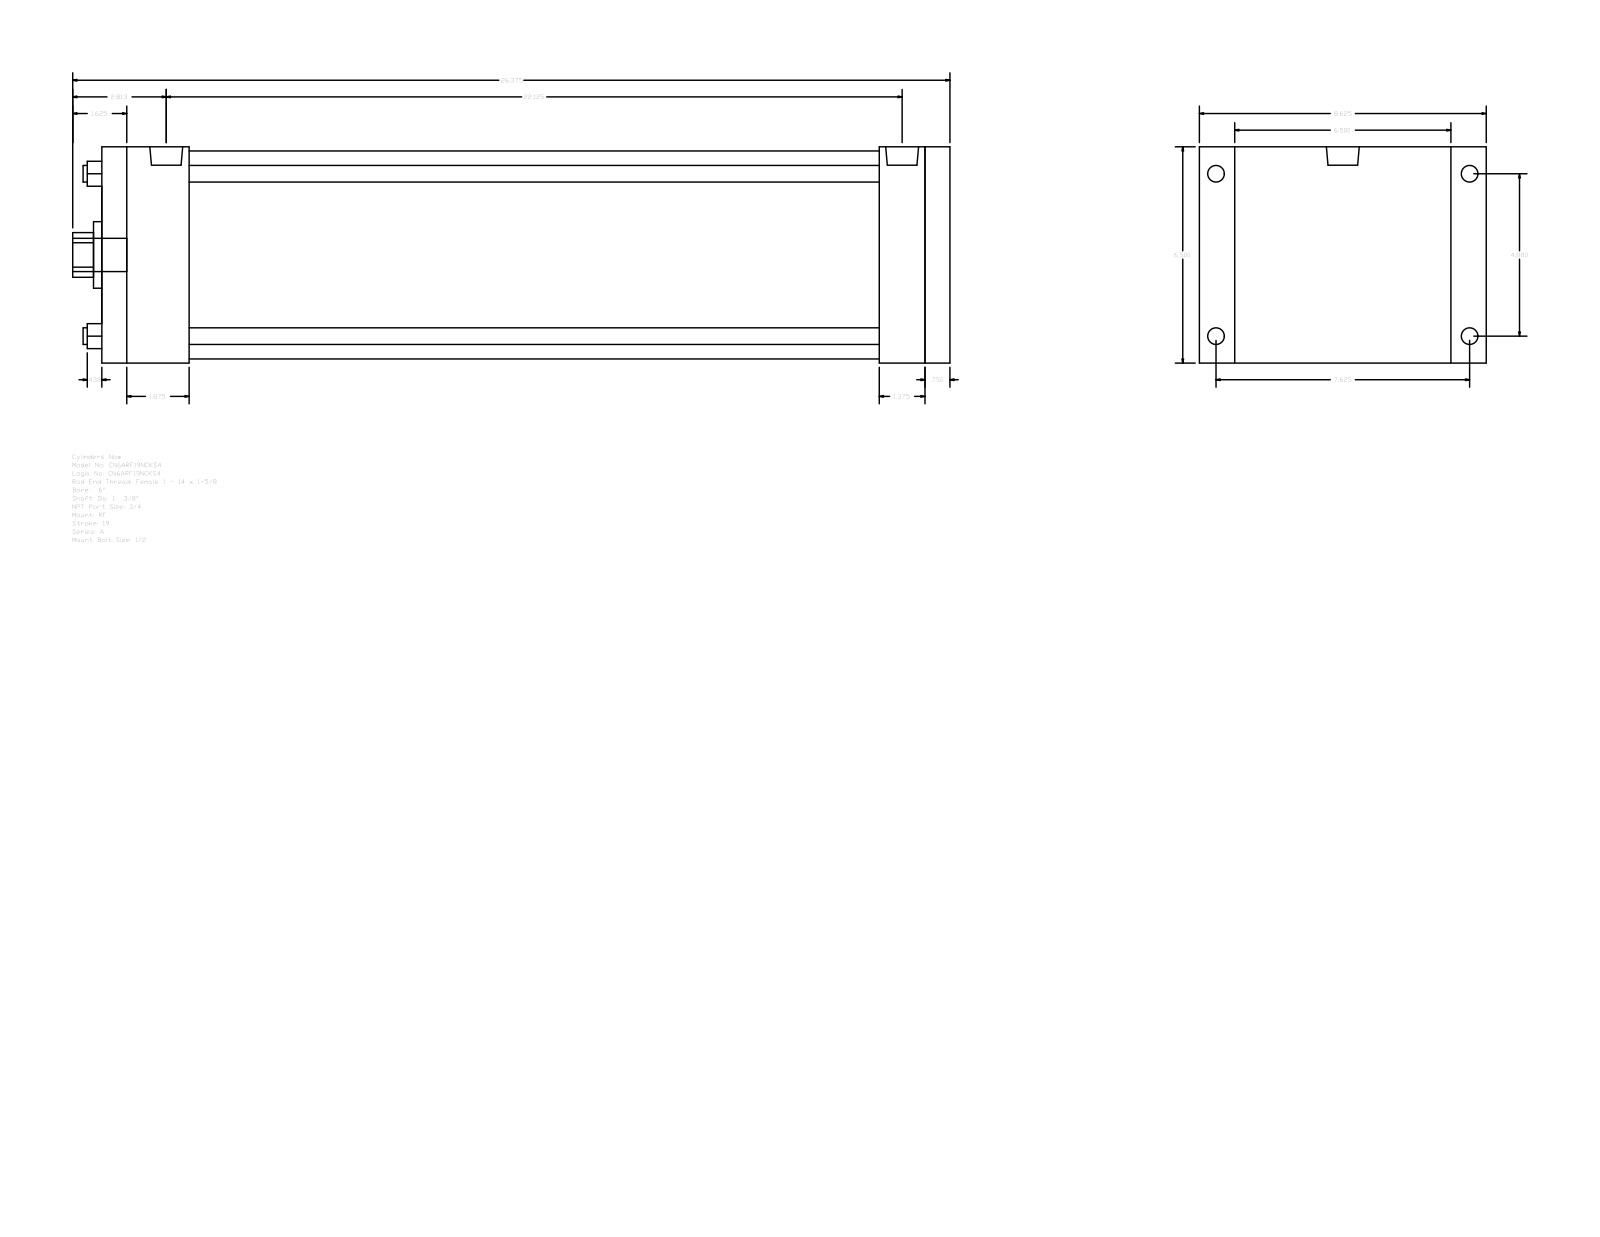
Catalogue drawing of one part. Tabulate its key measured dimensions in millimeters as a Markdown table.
| quantity | value |
| --- | --- |
| part name | A_RF__0600_1.375 |
| STEP written by | GSSL Pune (CONFIG_CONTROL_DESIGN) |
| units | millimeters |
| bodies | 0 solids, 92 faces (64 planar, 28 cylindrical, 0 other) |
| overall size | 669.92 × 219.07 × 165.1 |
| round holes (diameter × count) | 12.7 × 4, 34.92 × 1, 50.8 × 1, 158.75 × 1 |
| round bosses / shafts (diameter × count) | 15.08 × 4, 12.7 × 4, 25.12 × 2, 25.4 × 1 |
| partial cylindrical surfaces (radius × count) | 17.06 × 1 |
| main face-to-face distances | 165.1, 647.69, 19.04, 628.65, 66.67, 561.98, 581.02, 593.72, 527.05, 34.93 |
| hole center spacings | 87.65, 123.96, 175.31 |
